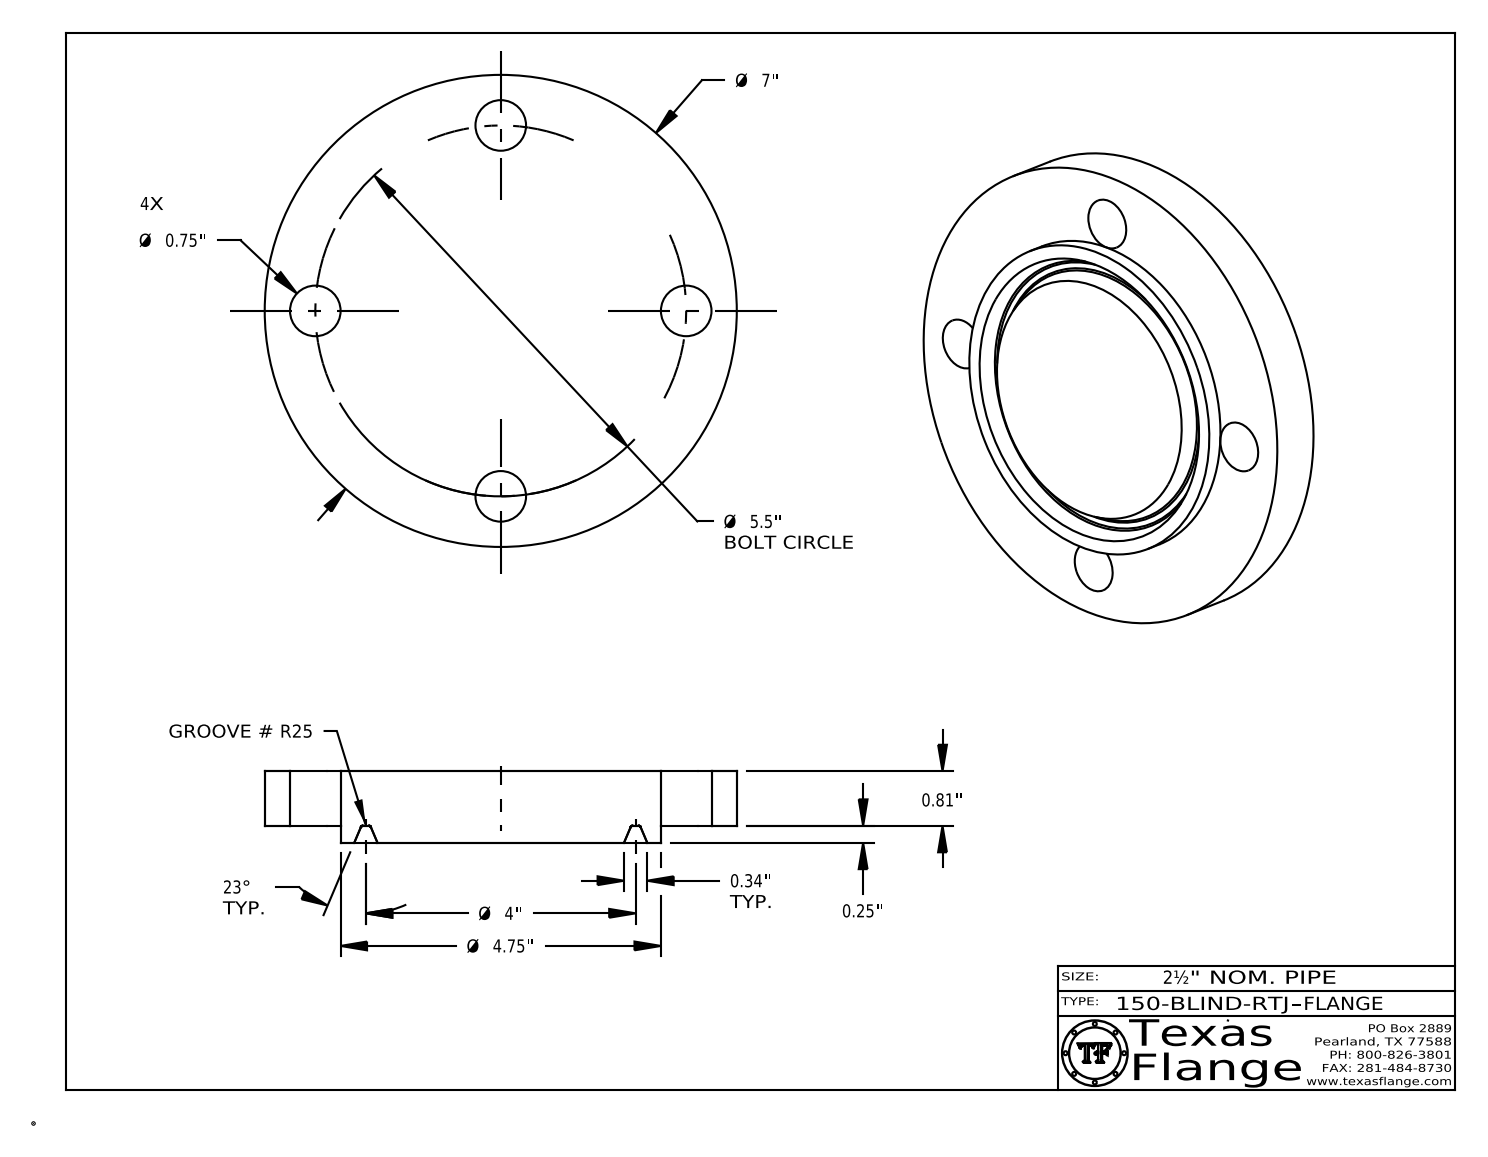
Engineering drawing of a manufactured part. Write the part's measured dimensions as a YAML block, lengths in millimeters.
part_name: "150-BLIND-RTJ"
step_written_by: "CATIA V5 STEP AP214 (AUTOMOTIVE_DESIGN)"
units: millimeters
bodies: {solids: 1, faces: 410, planar: 370, cylindrical: 32, other: 8}
overall_size: [177.8, 177.8, 26.9]
volume: 547800
surface_area: 68840
round_holes:
  - {diameter: 19.1, count: 4}
  - {diameter: 12.6, count: 1}
round_bosses_or_shafts:
  - {diameter: 0.8, count: 8}
  - {diameter: 177.8, count: 1}
  - {diameter: 120.7, count: 1}
  - {diameter: 9.9, count: 1}
face_to_face_distances: [20.6, 6.4, 26.9, 26.5, 20.2, 0.4, 3.8, 3.7, 0.7, 2.4]
hole_center_spacings: [98.8, 53.5, 129.1, 139.7]
